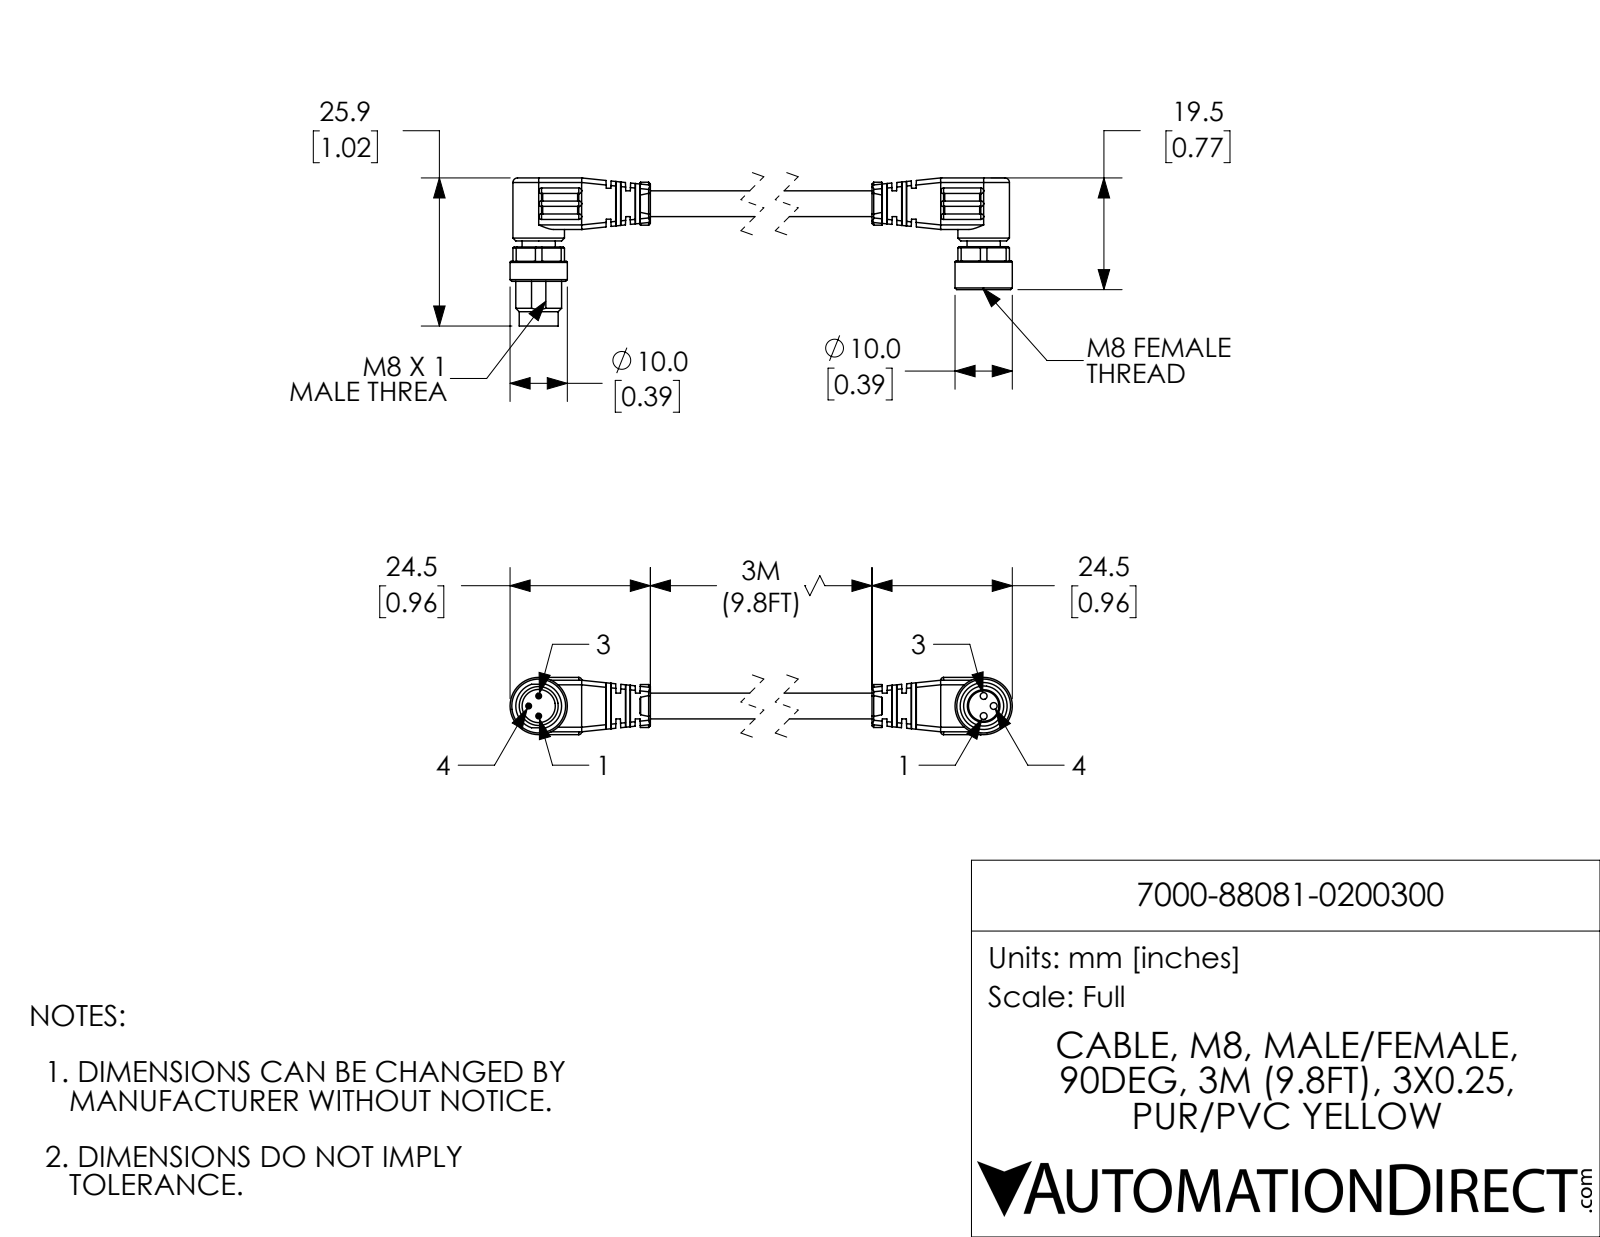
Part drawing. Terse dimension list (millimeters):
name: 7000-88081-0200300; 7000-88081-0200300_FEMALE; 7000-88081-0200300_MALE
written by: SolidWorks 2017 (AUTOMOTIVE_DESIGN)
unit: mm
bodies: 2 solids, 410 faces (190 planar, 144 cylindrical, 76 other)
size: 101 × 25.9 × 10
volume: 5 190 mm³; area: 3 909 mm²
holes: 3× ⌀1.2, 1× ⌀5.8, 1× ⌀7
bosses: 3× ⌀1, 2× ⌀10, 2× ⌀9, 1× ⌀8, 1× ⌀6.8, 1× ⌀5.8, 1× ⌀5.7, 1× ⌀4.5
rounds: 12× R0.8, 8× R0.2, 6× R0.5, 2× R4.9, 1× R3.8
face distances: 1, 9, 1.1, 6.8, 9.2, 2.3, 0.6, 3.4, 12, 59.8
hole spacings: 1.8, 2.5, 91, 3.5, 91, 92.8
